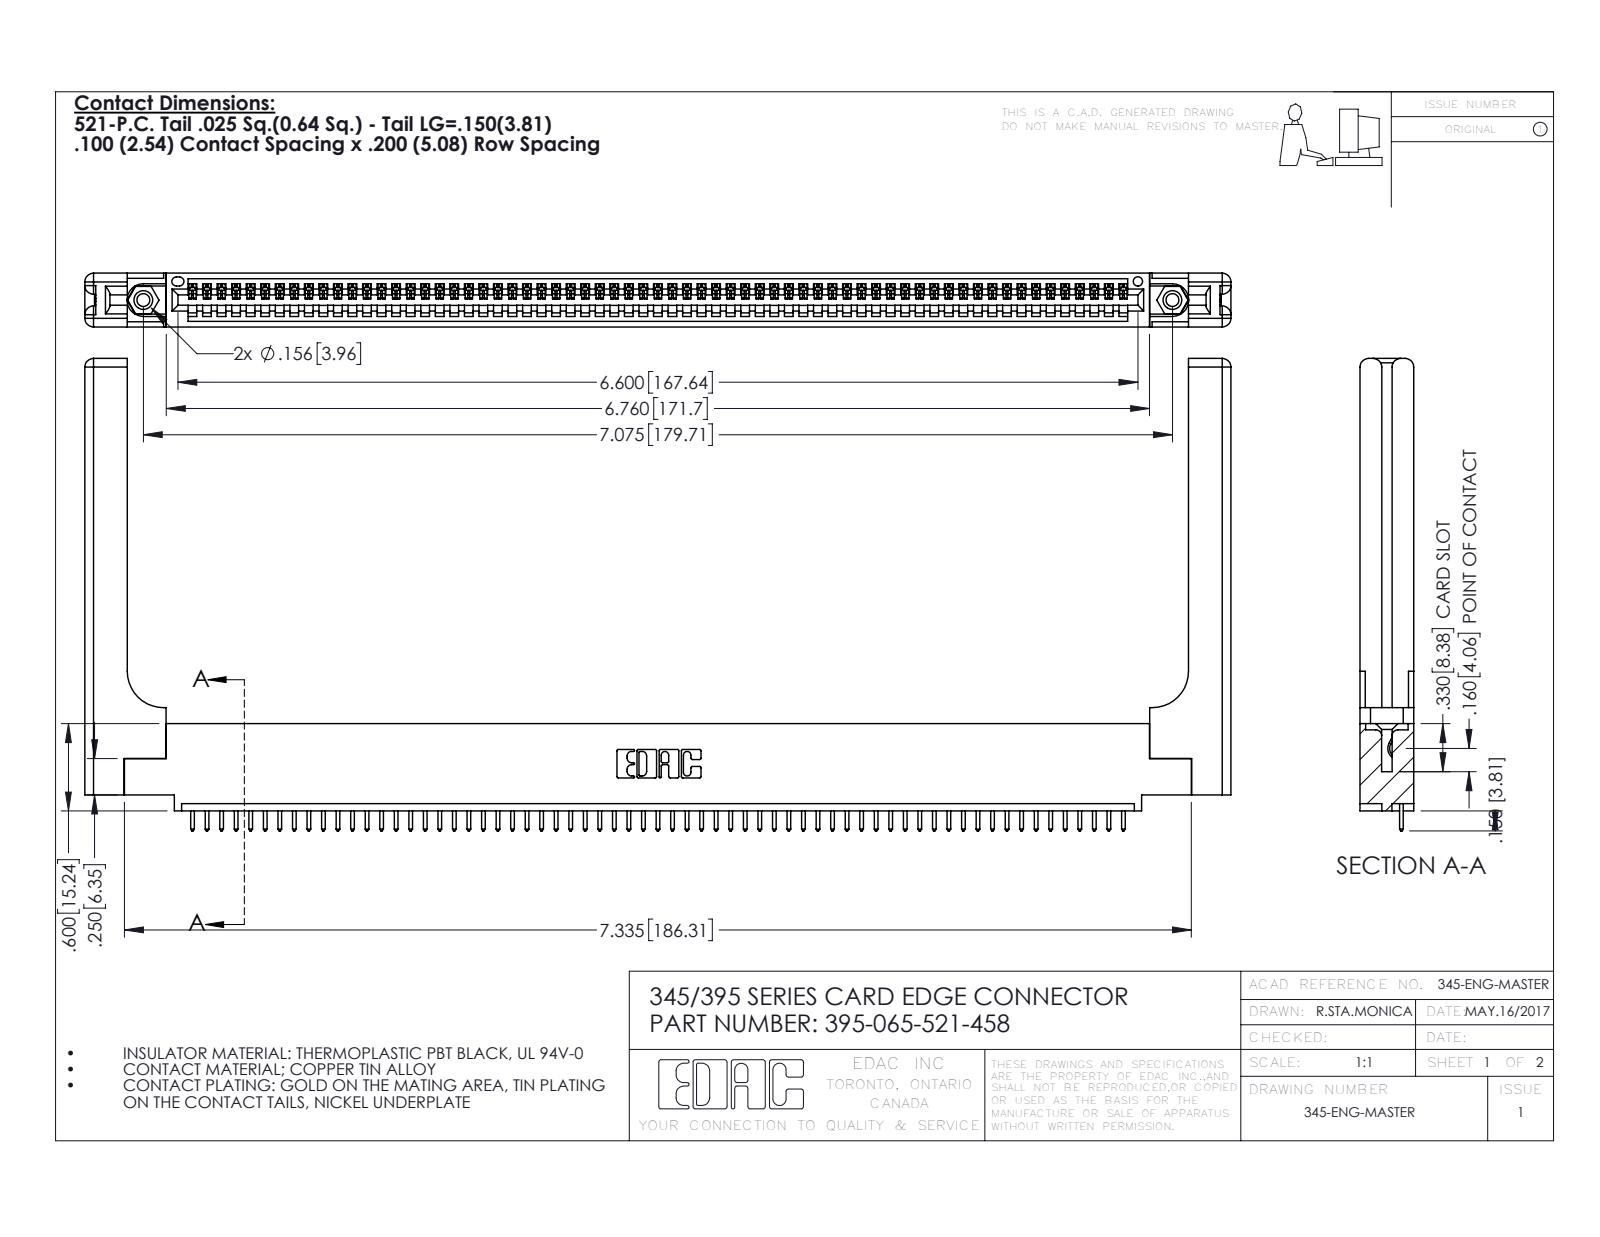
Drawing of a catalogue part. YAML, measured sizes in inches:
part_name: "345-220-058_345-220-058; 395-065-521-458; 345-292-001_345-293-121; 345-250-001_345-250-001-102 (+1 more)"
step_written_by: "SolidWorks 2016 (CONFIG_CONTROL_DESIGN)"
units: inches
bodies: {solids: 70, faces: 4156, planar: 2832, cylindrical: 1264, other: 60}
overall_size: [7.879, 3.247, 0.37]
volume: 1.675
surface_area: 46.72
round_holes:
  - {diameter: 0.089, count: 2}
  - {diameter: 0.125, count: 2}
  - {diameter: 0.156, count: 2}
  - {diameter: 0.064, count: 1}
round_bosses_or_shafts:
  - {diameter: 0.155, count: 2}
partial_cylinders:
  - {radius: 0.006, count: 130}
  - {radius: 0.01, count: 130}
  - {radius: 0.01, count: 22}
  - {radius: 0.06, count: 16}
  - {radius: 0.007, count: 6}
  - {radius: 0.031, count: 6}
  - {radius: 0.026, count: 3}
  - {radius: 0.03, count: 2}
face_to_face_distances: [0.072, 0.37, 0.298, 0.098, 0.272, 0.025, 0.2, 0.225, 0.148, 0.15]
hole_center_spacings: [0.27, 6.839, 7.075]
